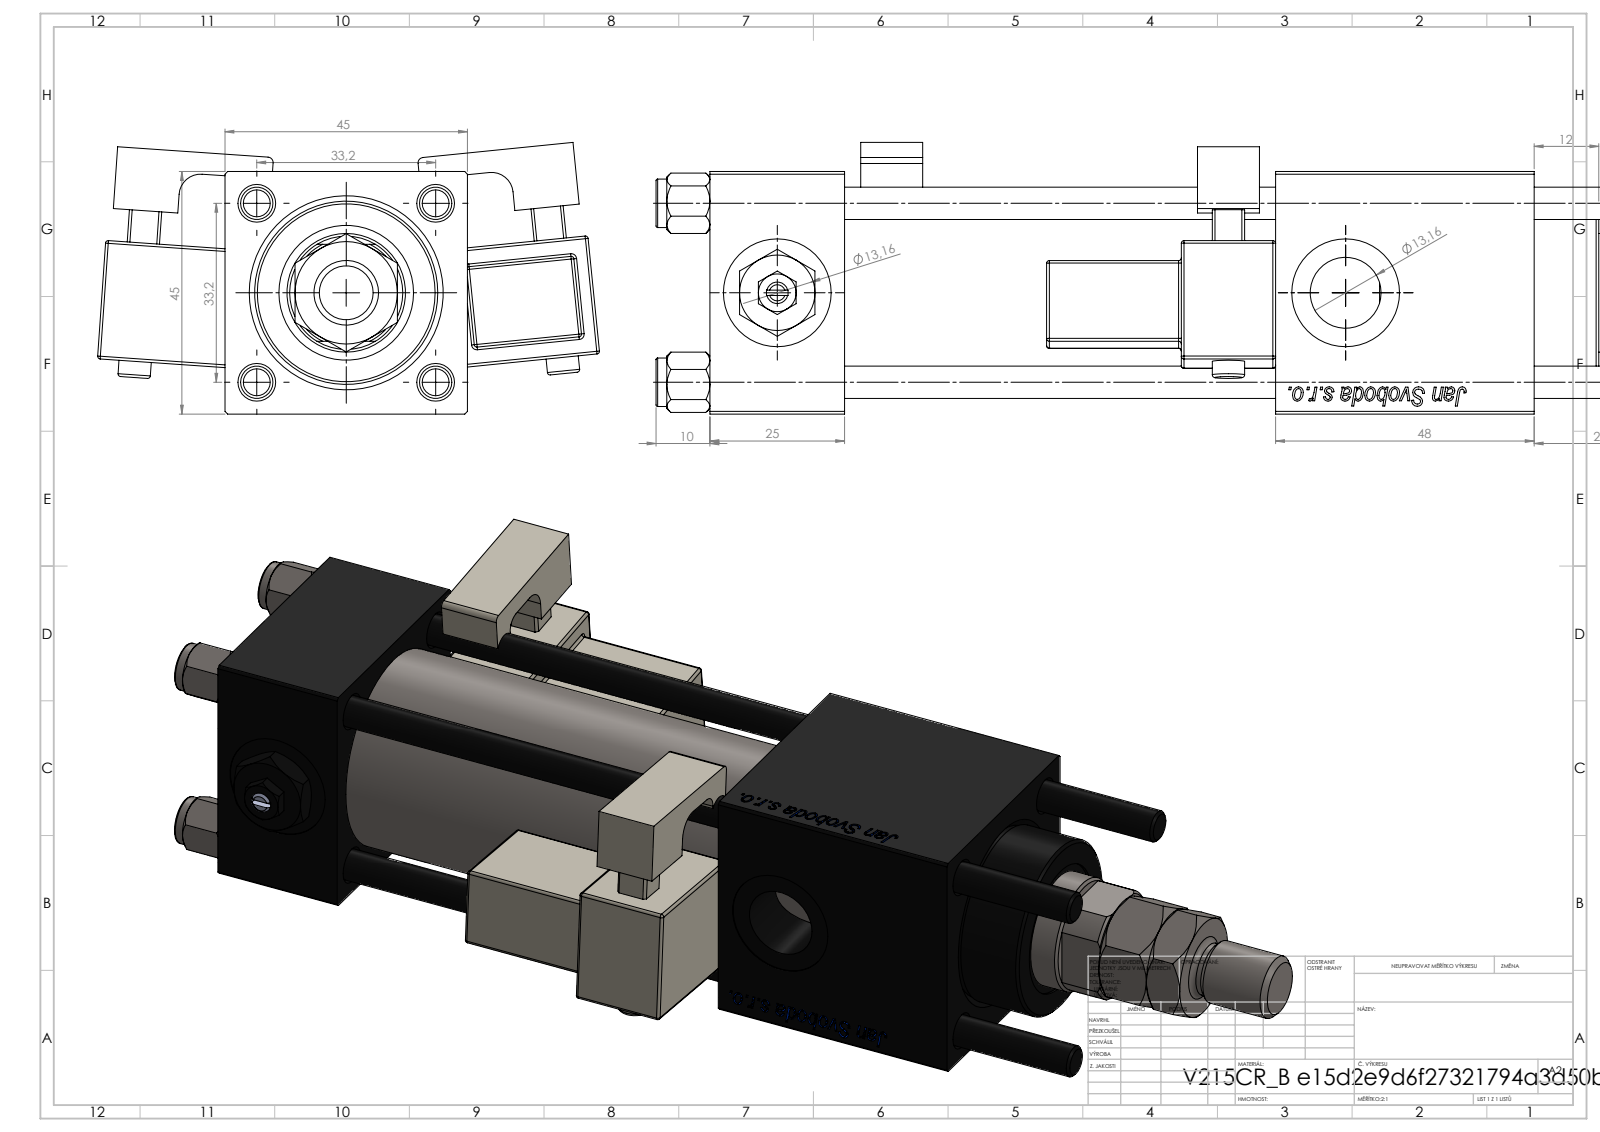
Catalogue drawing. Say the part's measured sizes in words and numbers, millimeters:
The part is named "V215CR_VCP_B; V215CR_B-1; V215_VC_A; MTA (+4 more)". Its 3-D file was written by "SolidWorks 2019 (CONFIG_CONTROL_DESIGN)". It is 15 solids with 1415 faces: 531 planar, 148 cylindrical and 736 other. Overall it measures 221 by 93.14 by 50.4 millimeters. Its volume is 285 811 cubic millimeters and its surface area 103 119 square millimeters. Round holes: 4 of diameter 6, 2 of diameter 7, 2 of diameter 13.16, 2 of diameter 20, 1 of diameter 10.5, 1 of diameter 22, 1 of diameter 24, 1 of diameter 25, 1 of diameter 32, 1 of diameter 33. Round bosses or shafts: 4 of diameter 9, 2 of diameter 6, 1 of diameter 38, 1 of diameter 34, 1 of diameter 12, 1 of diameter 10. Partial cylindrical surfaces (rounded edges, fillets, slot ends): 48 of radius 0.5, 2 of radius 1, 2 of radius 2.5, 2 of radius 4, 1 of radius 10.5. The main face-to-face distances are 45, 25, 105, 80, 62.5, 153, 3, 48, 20, 17.5. The hole center spacings are 23.48, 33.2, 46.95, 105.5.
